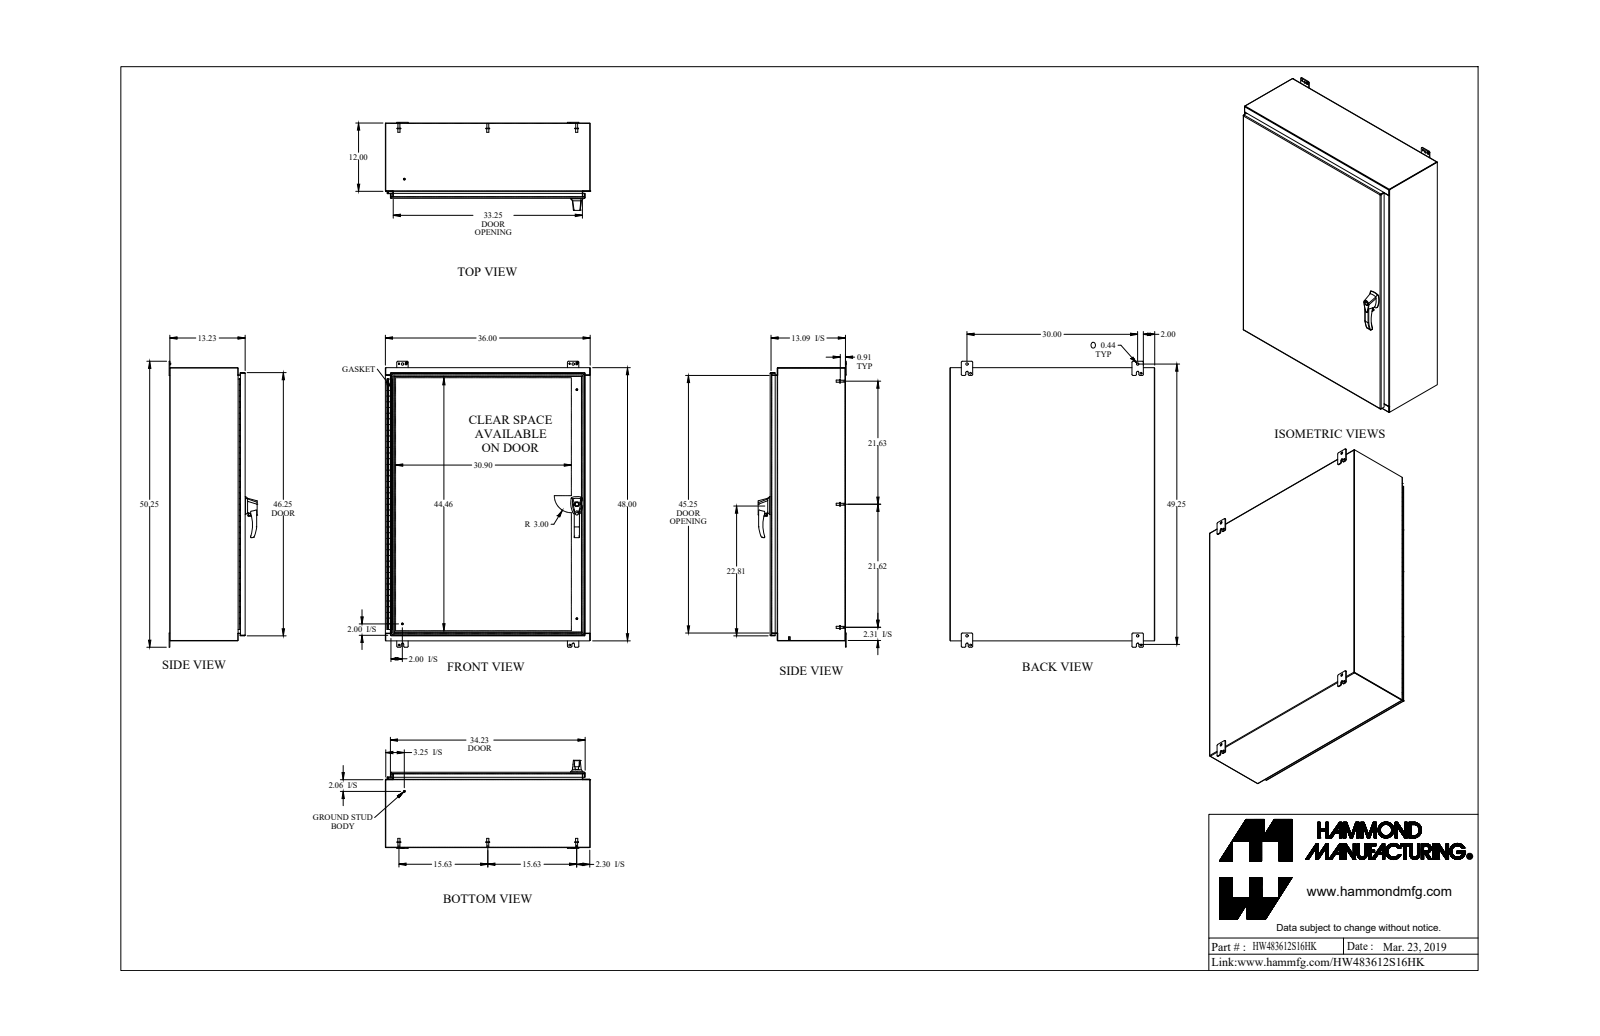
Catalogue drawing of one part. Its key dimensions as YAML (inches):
part_name: "HW483612S16HK"
step_written_by: "SolidWorks 2018 (AUTOMOTIVE_DESIGN)"
units: inches
bodies: {solids: 47, faces: 1584, planar: 736, cylindrical: 712, other: 136}
overall_size: [50.25, 36, 15.473]
volume: 507.1
surface_area: 12571
round_holes:
  - {diameter: 0.176, count: 6}
  - {diameter: 0.313, count: 4}
  - {diameter: 0.25, count: 3}
  - {diameter: 0.265, count: 3}
  - {diameter: 0.413, count: 3}
  - {diameter: 0.196, count: 2}
  - {diameter: 0.256, count: 2}
  - {diameter: 0.394, count: 2}
  - {diameter: 0.437, count: 2}
  - {diameter: 0.11, count: 1}
  - {diameter: 0.233, count: 1}
  - {diameter: 0.33, count: 1}
round_bosses_or_shafts:
  - {diameter: 0.375, count: 13}
  - {diameter: 0.65, count: 8}
  - {diameter: 0.332, count: 8}
  - {diameter: 0.25, count: 7}
  - {diameter: 0.156, count: 6}
  - {diameter: 1, count: 3}
  - {diameter: 0.63, count: 2}
  - {diameter: 0.51, count: 2}
partial_cylinders:
  - {radius: 0.25, count: 27}
  - {radius: 0.188, count: 20}
  - {radius: 0.036, count: 14}
  - {radius: 0.108, count: 14}
  - {radius: 0.06, count: 12}
  - {radius: 0.125, count: 9}
  - {radius: 0.218, count: 8}
  - {radius: 0.03, count: 6}
face_to_face_distances: [0.072, 13.138, 13.066, 0.095, 13.233, 13.161, 35.928, 47.928, 35.856, 36]
hole_center_spacings: [20.118, 20.119, 40.237, 1.11, 1.111, 20.119, 20.887, 30]
